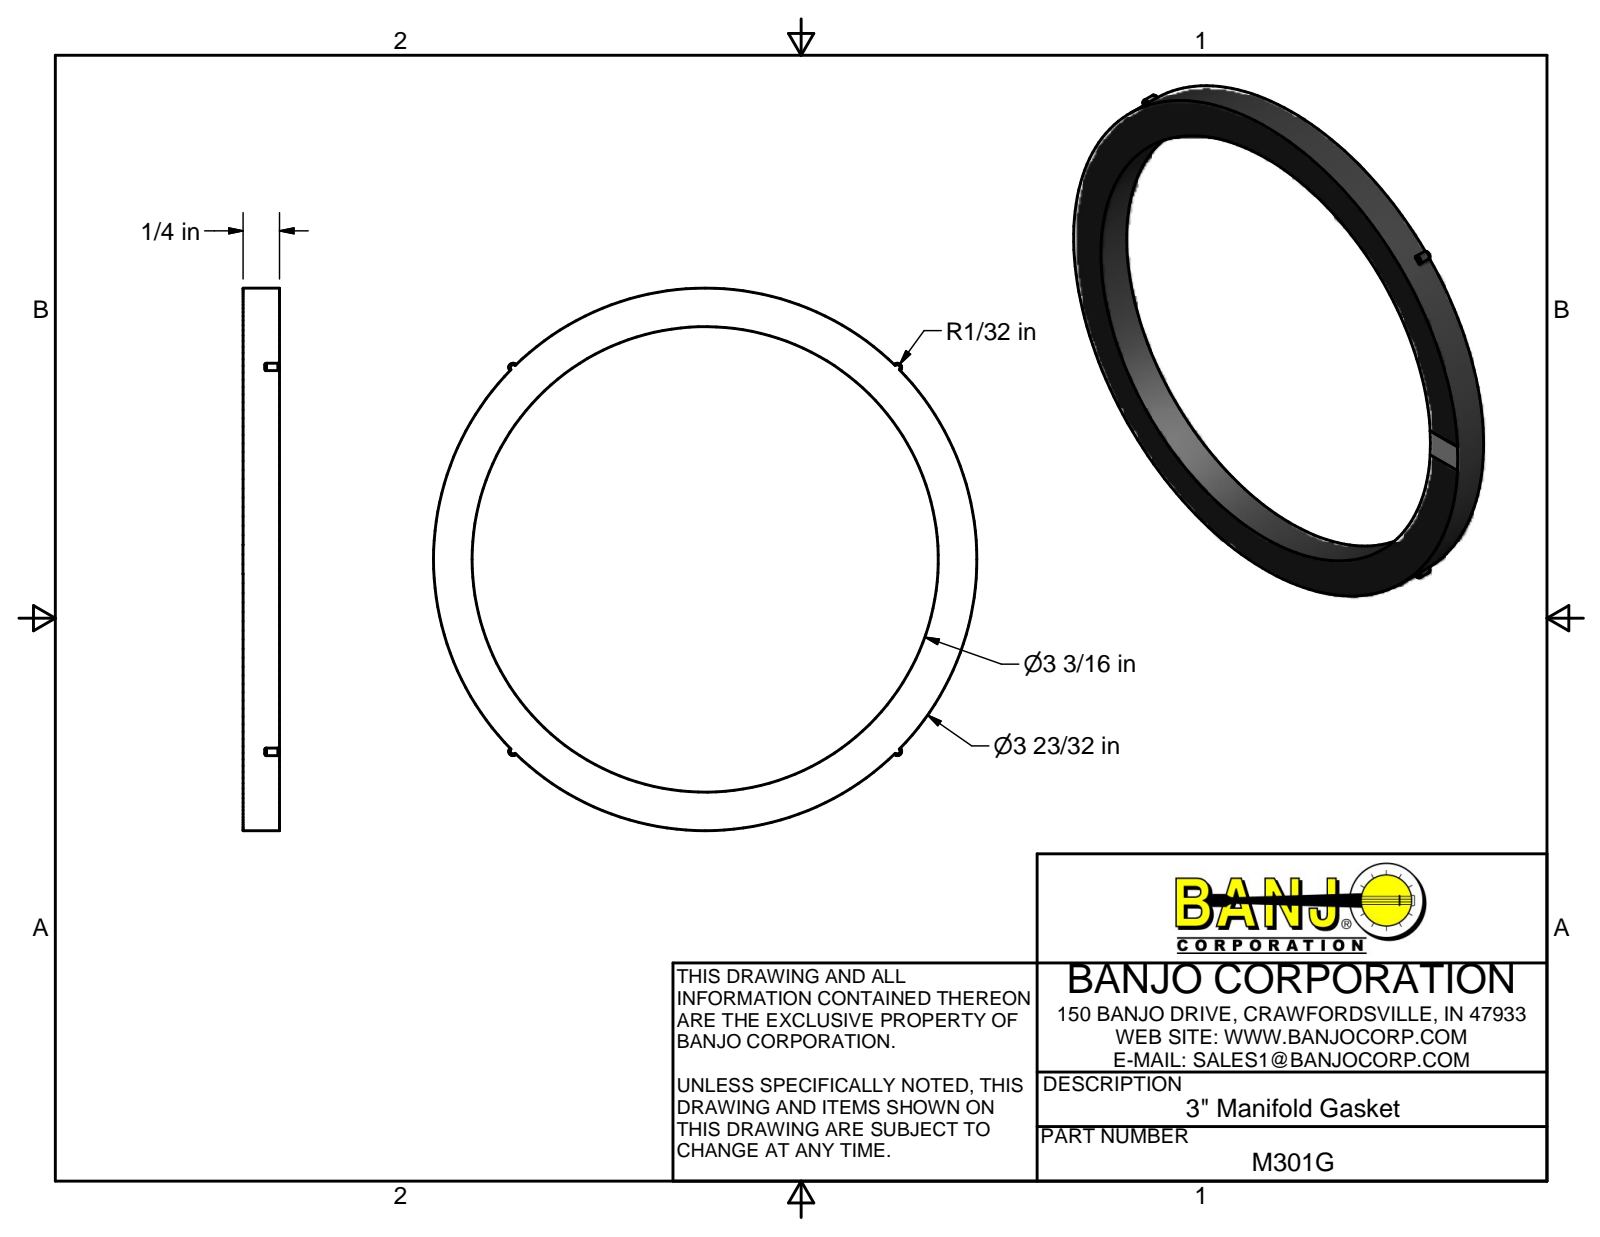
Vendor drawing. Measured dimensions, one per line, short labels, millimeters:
name: M301G
written by: Autodesk Inventor 2011 (AUTOMOTIVE_DESIGN)
unit: mm
bodies: 1 solid, 23 faces (9 planar, 6 cylindrical, 8 other)
size: 94.7 × 94.7 × 6.4
volume: 11 800 mm³; area: 7 252 mm²
holes: 1× ⌀81.3
bosses: 1× ⌀94.7
rounds: 4× R0.8
face distances: 6.4, 6.4, 3.8, 3.8, 2.5, 5.1
